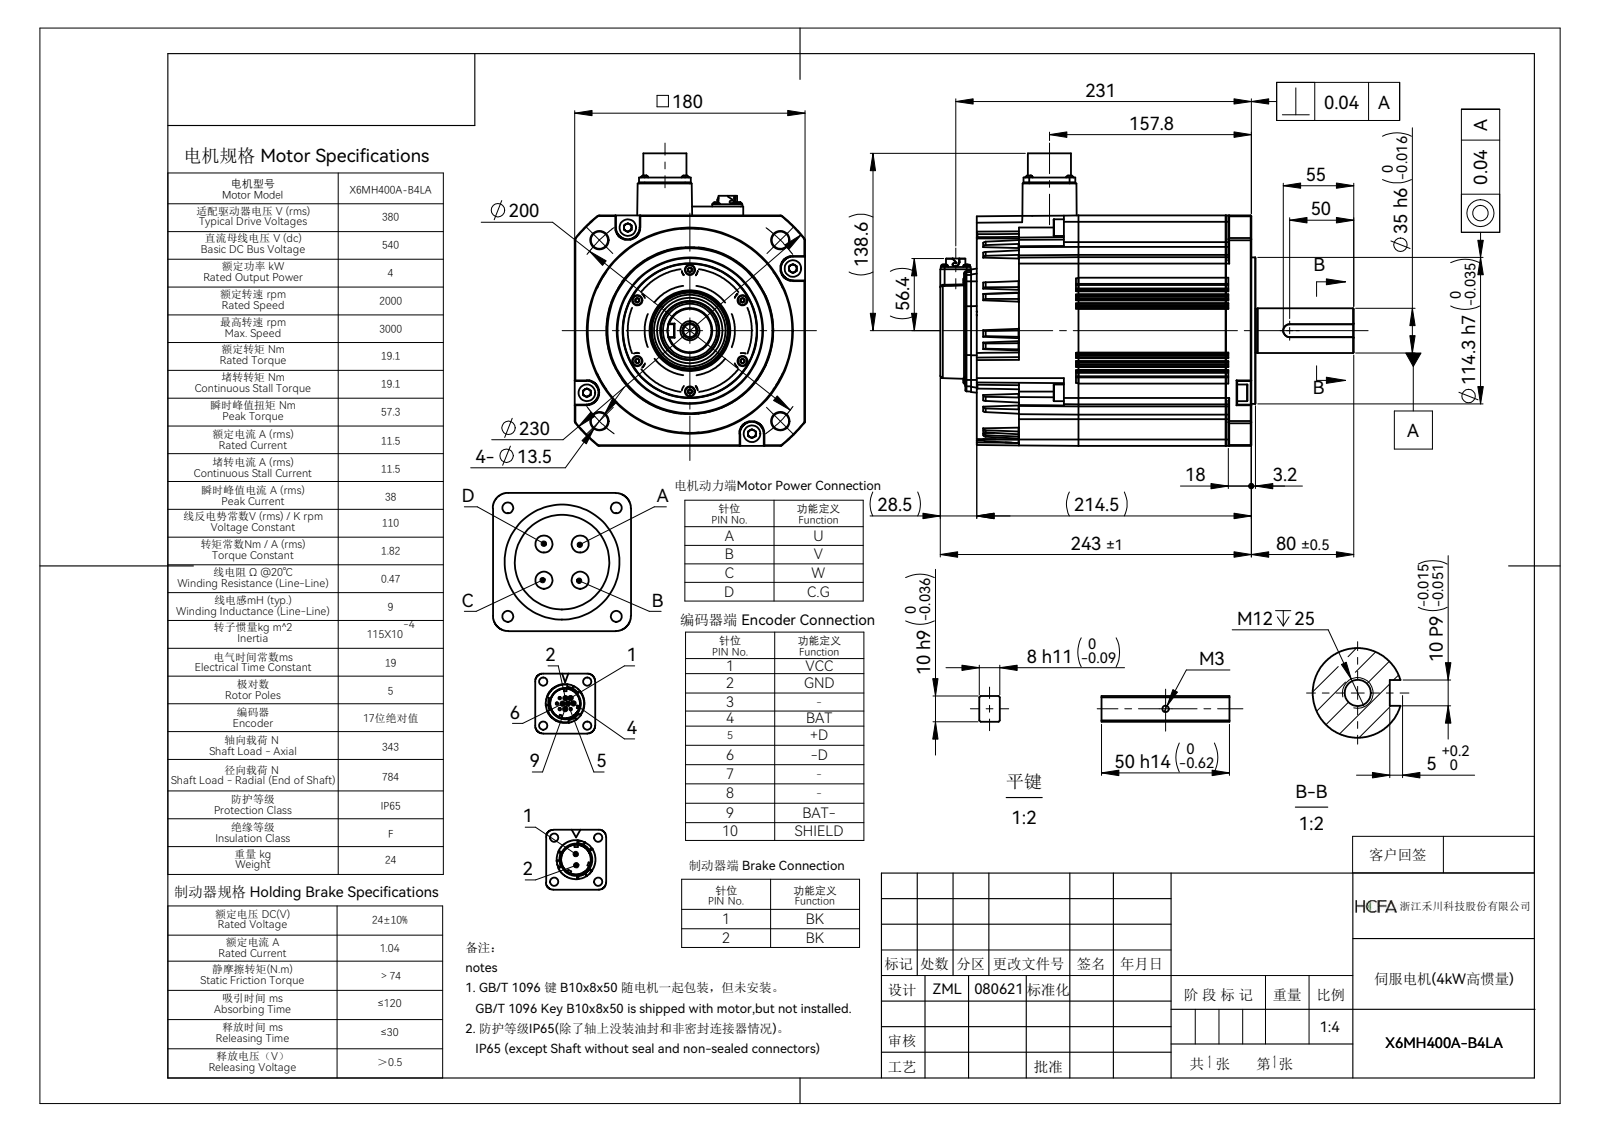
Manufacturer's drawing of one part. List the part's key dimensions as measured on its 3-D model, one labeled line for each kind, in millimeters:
Part name (STEP PRODUCT): SV-X2MH400A-B4LA
STEP written by: SolidWorks 2016 (CONFIG_CONTROL_DESIGN)
Units: millimetres
Bodies: 2 solids, 2966 faces (1080 planar, 954 cylindrical, 932 other)
Overall size (bounding box): 323 × 228.55 × 180
Volume: 6 157 000 mm³ · Surface area: 288 400 mm²
Round holes (diameter × count): ⌀2.5 ×20, ⌀3.2 ×12, ⌀8 ×6, ⌀3.5 ×4, ⌀13.5 ×4, ⌀12.2 ×3, ⌀16 ×3, ⌀1 ×2, ⌀11.6 ×2, ⌀5 ×1, ⌀5.5 ×1, ⌀10.2 ×1
Round bosses / shafts (diameter × count): ⌀5.7 ×12, ⌀3 ×12, ⌀1 ×10, ⌀7 ×6, ⌀13 ×5, ⌀5 ×4, ⌀2.9 ×4, ⌀2.4 ×4
Partial cylindrical surfaces — rounded edges, fillets, slot ends (radius × count): R0.5 ×111, R1 ×58, R5 ×28, R0.55 ×16, R2 ×16, R3 ×8, R4 ×6, R0.2 ×4
Main face-to-face distances: 180, 32.5, 147.5, 214.5, 115, 4, 7, 6.97, 51.96, 210.5
Hole centre spacings: 47.5, 12.16, 17.2, 114.13, 63.79, 78.87, 5.96, 10.75
